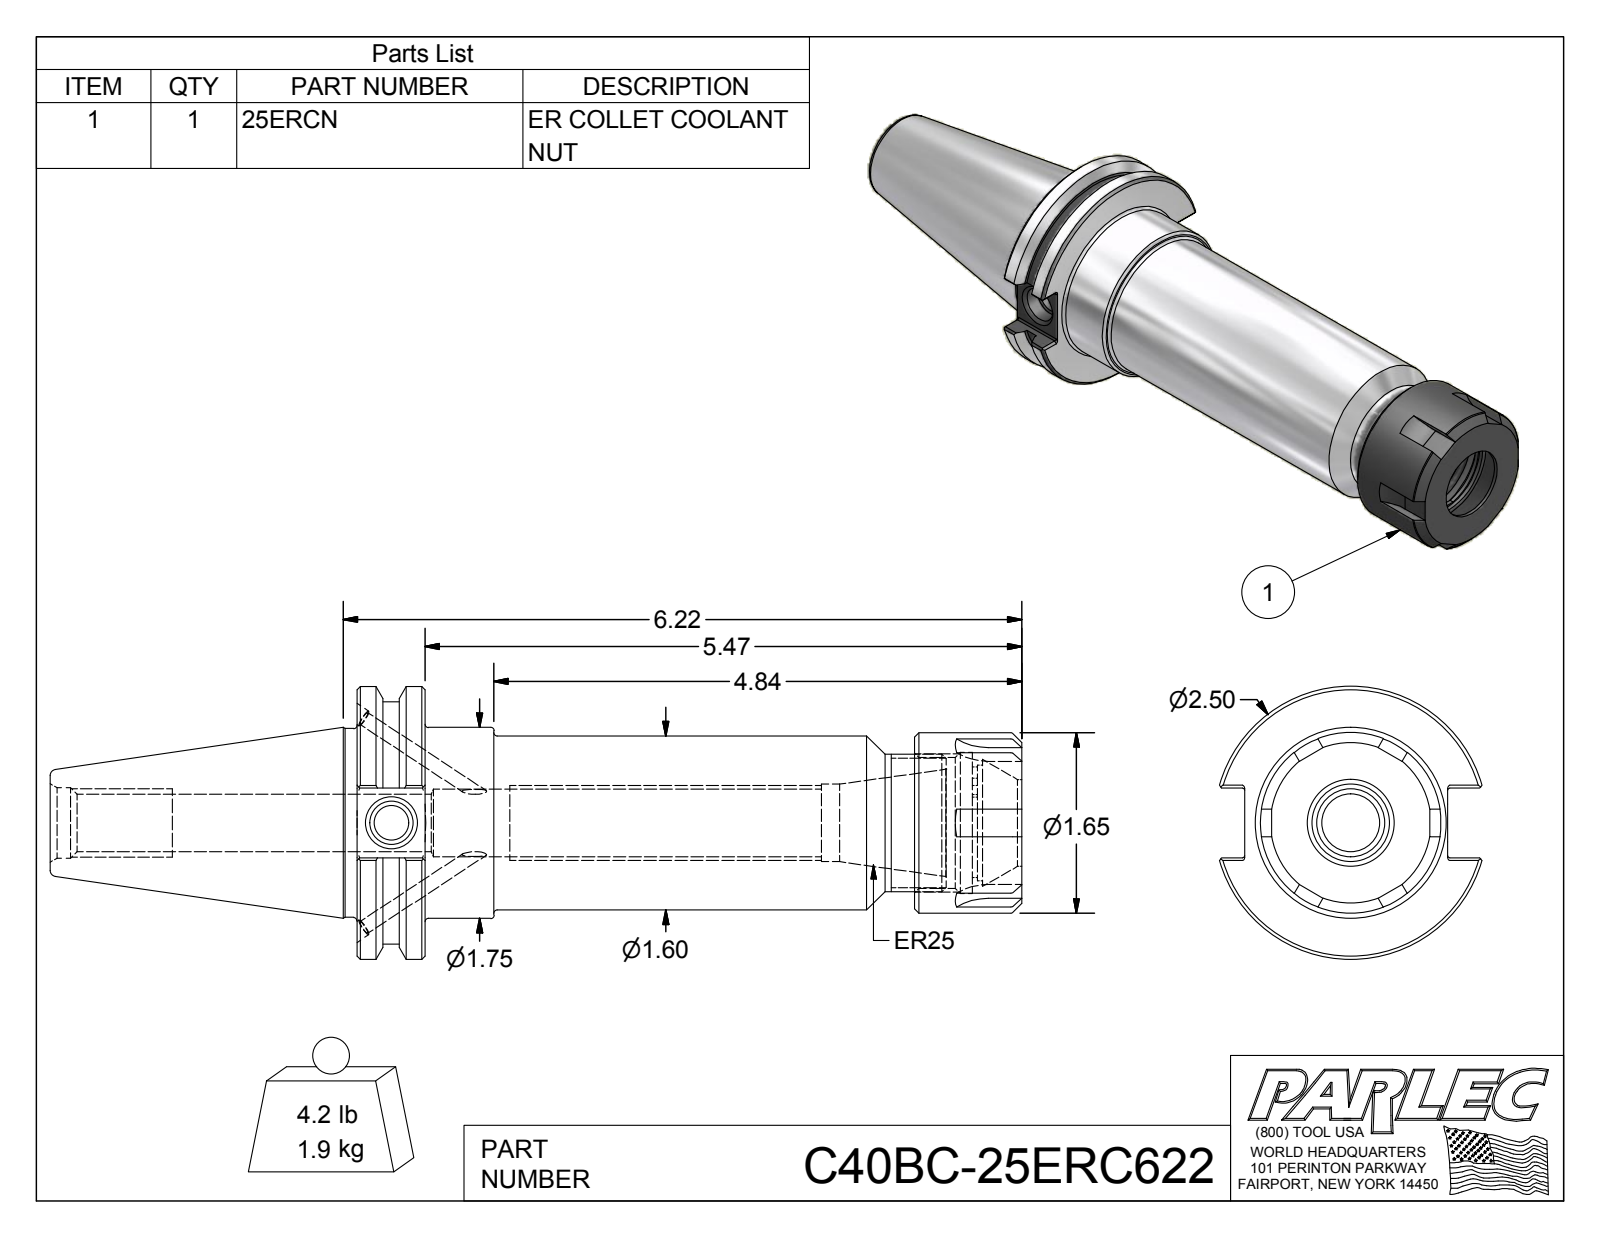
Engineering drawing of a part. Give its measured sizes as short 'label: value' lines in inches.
name: C40BC-25ERC622; C40BC-25ER6-1; 25ERCN
written by: Autodesk Inventor 2012 (AUTOMOTIVE_DESIGN)
unit: in
bodies: 2 solids, 151 faces (63 planar, 48 cylindrical, 40 other)
size: 8.908 × 2.5 × 2.403
volume: 14.73 in³; area: 76.93 in²
holes: 2× ⌀0.13, 2× ⌀0.161, 1× ⌀0.315, 1× ⌀0.399, 1× ⌀0.527, 1× ⌀0.62, 1× ⌀0.648, 1× ⌀0.71, 1× ⌀0.794, 1× ⌀1.057, 1× ⌀1.201, 1× ⌀1.294
bosses: 1× ⌀2.5, 1× ⌀2.219, 1× ⌀1.75, 1× ⌀1.73, 1× ⌀1.654, 1× ⌀1.595, 1× ⌀1.26
rounds: 12× R0.02, 6× R0.5, 1× R0.472, 1× R0.515
face distances: 0.625, 6.095, 5.47, 5.111, 4.486, 0.984, 5.643, 5.017, 0.531, 0.453
